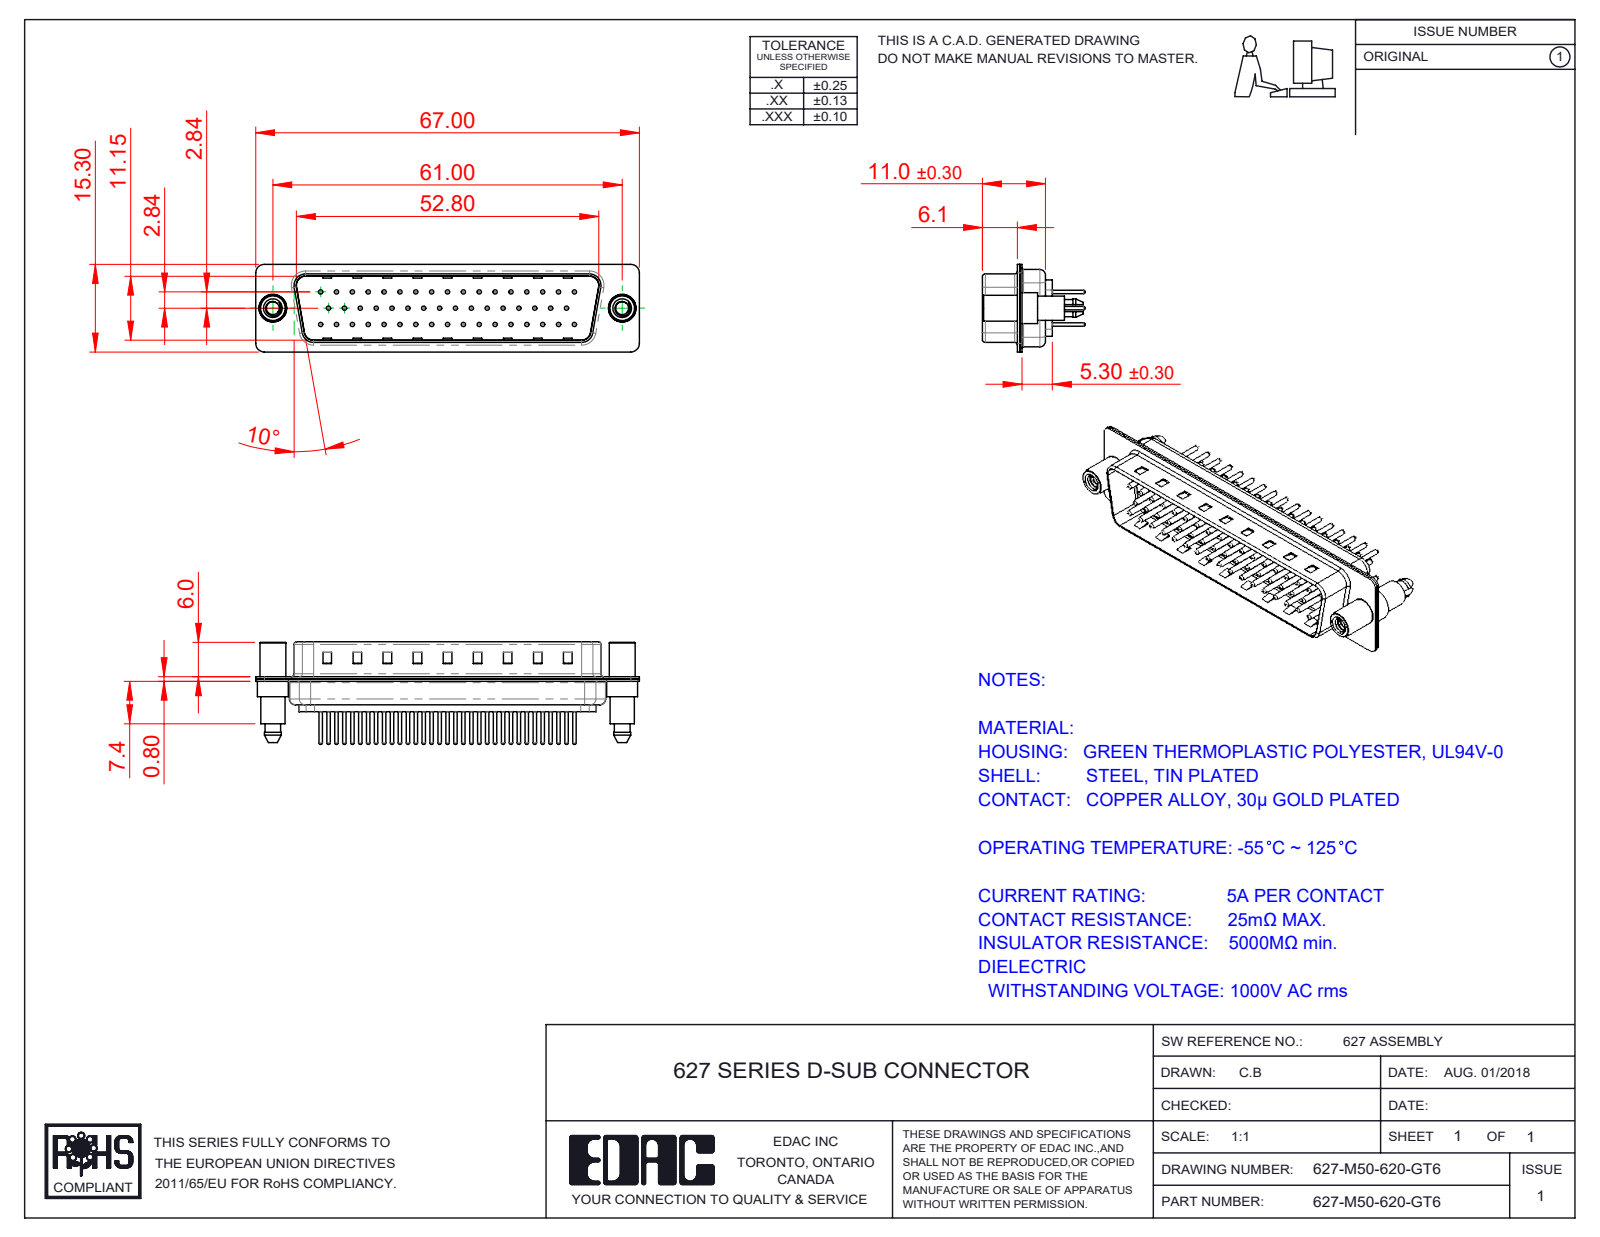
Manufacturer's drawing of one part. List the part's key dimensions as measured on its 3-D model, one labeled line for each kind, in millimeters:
Part name (STEP PRODUCT): 627M Housing_50 Contacts; 627M Contact Row 3_20; 627M Shell Front_50 Contacts; 627M Contact Row 1_20 (+4 more)
STEP written by: SolidWorks 2020 (CONFIG_CONTROL_DESIGN)
Units: millimetres
Bodies: 55 solids, 2314 faces (571 planar, 869 cylindrical, 874 other)
Overall size (bounding box): 67 × 17.9 × 15.3
Volume: 4 863 mm³ · Surface area: 11 167 mm²
Round holes (diameter × count): ⌀0.75 ×50, ⌀1.6 ×50, ⌀2 ×50, ⌀2.26 ×2, ⌀4 ×2, ⌀4.8 ×2
Round bosses / shafts (diameter × count): ⌀1.5 ×50, ⌀0.6 ×50, ⌀5.4 ×2, ⌀4.9 ×2, ⌀4.5 ×2, ⌀4.25 ×2
Partial cylindrical surfaces — rounded edges, fillets, slot ends (radius × count): R1.5 ×18, R2 ×12, R1.6 ×10, R0.5 ×8, R0.25 ×4, R0.6 ×4, R0.65 ×4, R0.9 ×4
Main face-to-face distances: 0.4, 11.55, 5.7, 6.1, 0.78, 0.77, 12.33, 5.3, 12.32, 13.1
Hole centre spacings: 3.16, 2.77, 5.54, 8.31, 11.08, 13.85, 16.62, 5.03
